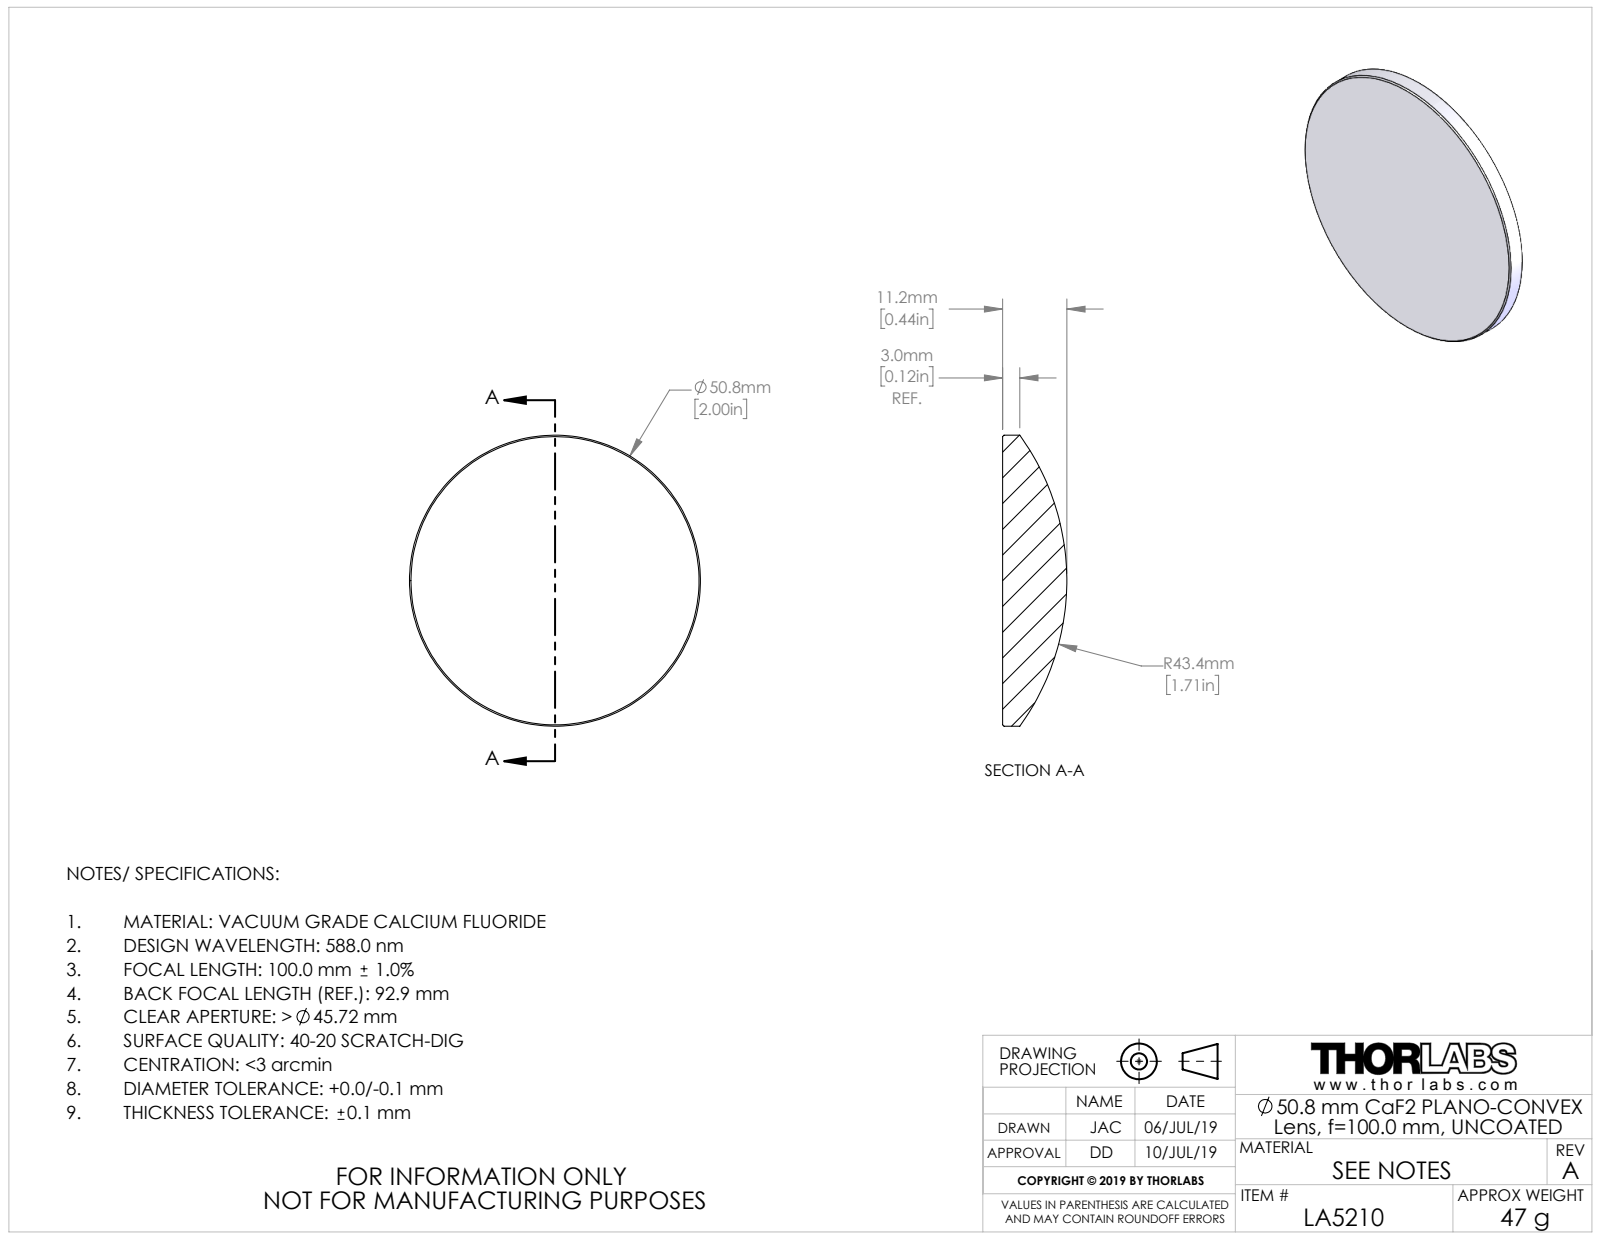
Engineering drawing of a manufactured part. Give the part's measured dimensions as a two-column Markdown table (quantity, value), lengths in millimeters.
| quantity | value |
| --- | --- |
| part name | TTN188096-E0W |
| STEP written by | SolidWorks 2018 (CONFIG_CONTROL_DESIGN) |
| units | millimeters |
| bodies | 1 solid, 7 faces (1 planar, 2 cylindrical, 4 other) |
| overall size | 50.8 × 50.8 × 11.21 |
| volume | 14 682 mm³ |
| surface area | 4 720 mm² |
| round bosses / shafts (diameter × count) | 50.8 × 1 |
